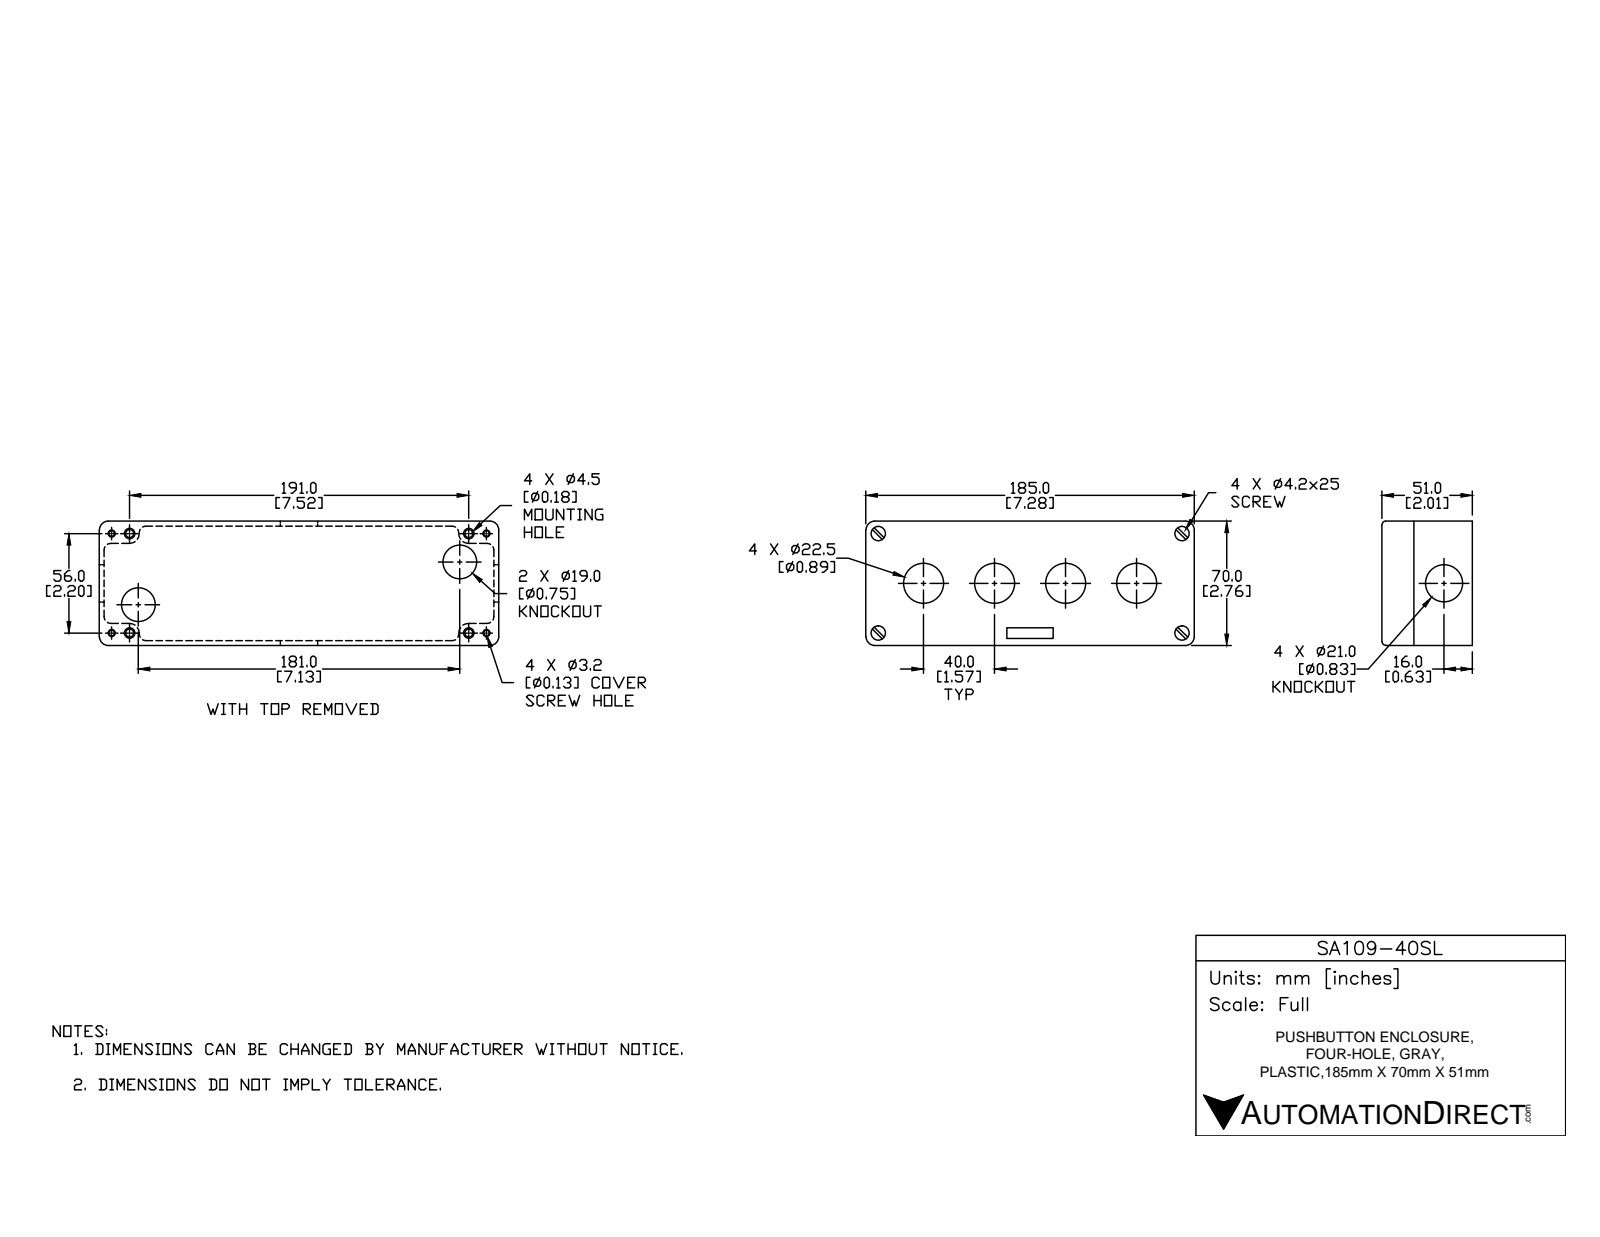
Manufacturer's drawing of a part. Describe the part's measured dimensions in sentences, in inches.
The part is named "SA109-40SL". Its 3-D file was written by "SolidWorks 2018 (AUTOMOTIVE_DESIGN)". It is 6 solids with 492 faces: 132 planar, 200 cylindrical and 160 other. Overall it measures 7.283 by 2.756 by 2.016 inches. Its volume is 10.63 cubic inches and its surface area 159.6 square inches. Round holes: 4 of diameter 0.126, 4 of diameter 0.165, 4 of diameter 0.177, 4 of diameter 0.295, 4 of diameter 0.315, 4 of diameter 0.886, 2 of diameter 0.094, 2 of diameter 0.748, 2 of diameter 0.827. Round bosses or shafts: 4 of diameter 0.291, 4 of diameter 0.11. Partial cylindrical surfaces (rounded edges, fillets, slot ends): 16 of radius 0.02, 8 of radius 0.041, 8 of radius 0.095, 4 of radius 0.039, 4 of radius 0.071, 4 of radius 0.197, 4 of radius 0.259, 4 of radius 0.323. The main face-to-face distances are 0.13, 0.098, 2.01, 1.911, 2.626, 2.756, 1.833, 0.079, 1.931, 0.085. The hole center spacings are 1.12, 6.339, 0.394, 1.26, 1.491, 2.205, 2.24, 2.447.
